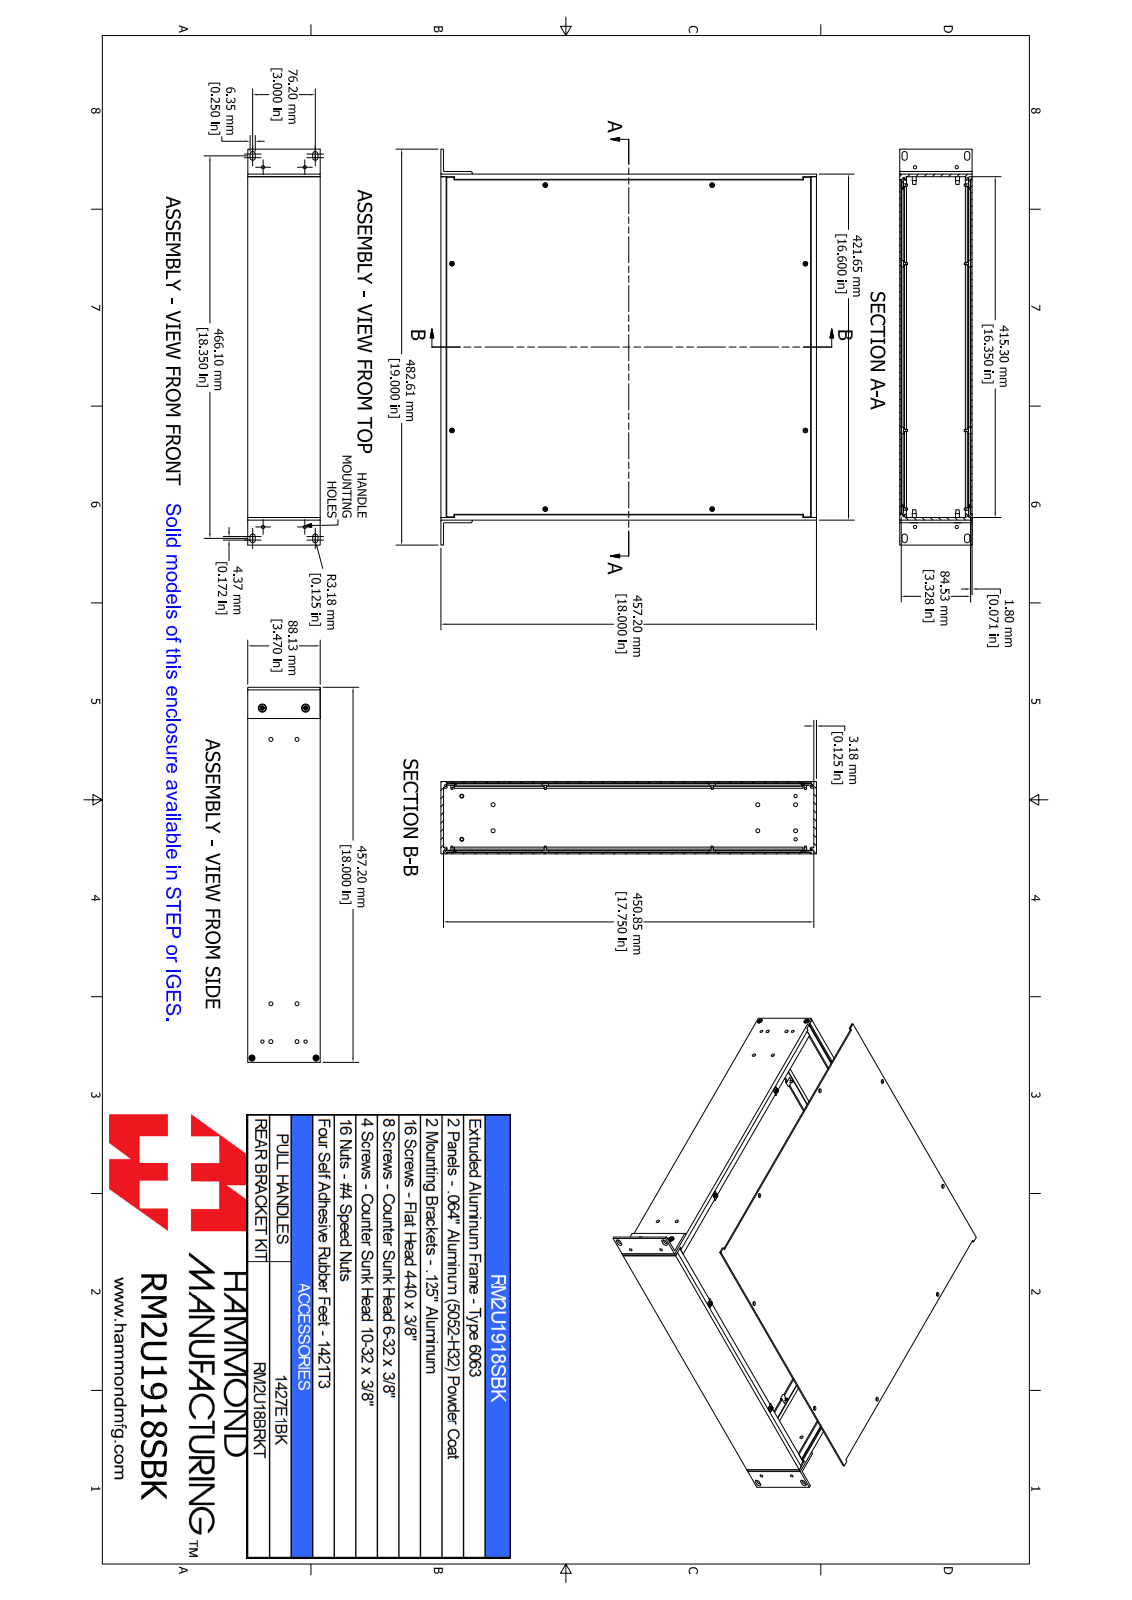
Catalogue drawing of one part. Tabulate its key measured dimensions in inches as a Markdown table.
| quantity | value |
| --- | --- |
| part name | RM2U1918SBK |
| STEP written by | SolidWorks 2021 (AUTOMOTIVE_DESIGN) |
| units | inches |
| bodies | 52 solids, 1364 faces (636 planar, 232 cylindrical, 496 other) |
| overall size | 19 × 18 × 3.471 |
| volume | 80.72 in³ |
| surface area | 1 858 in² |
| round holes (diameter × count) | 0.098 × 8, 0.118 × 8, 0.157 × 8, 0.157 × 8, 0.188 × 6, 0.159 × 4, 0.169 × 4, 0.169 × 4, 0.197 × 4 |
| round bosses / shafts (diameter × count) | 0.214 × 8, 0.112 × 8, 0.333 × 4, 0.238 × 4, 0.19 × 4, 0.138 × 4 |
| partial cylindrical surfaces (radius × count) | 0.125 × 16, 0.039 × 14, 0.049 × 8, 0.05 × 8, 0.038 × 6, 0.037 × 5, 0.079 × 2 |
| main face-to-face distances | 0.071, 3.399, 3.47, 3.328, 0.125, 0.125, 16.6, 16.476, 16.35, 18 |
| hole center spacings | 8, 13.031, 0.935, 1.555, 2.691, 5.851, 5.852, 12.594 |
